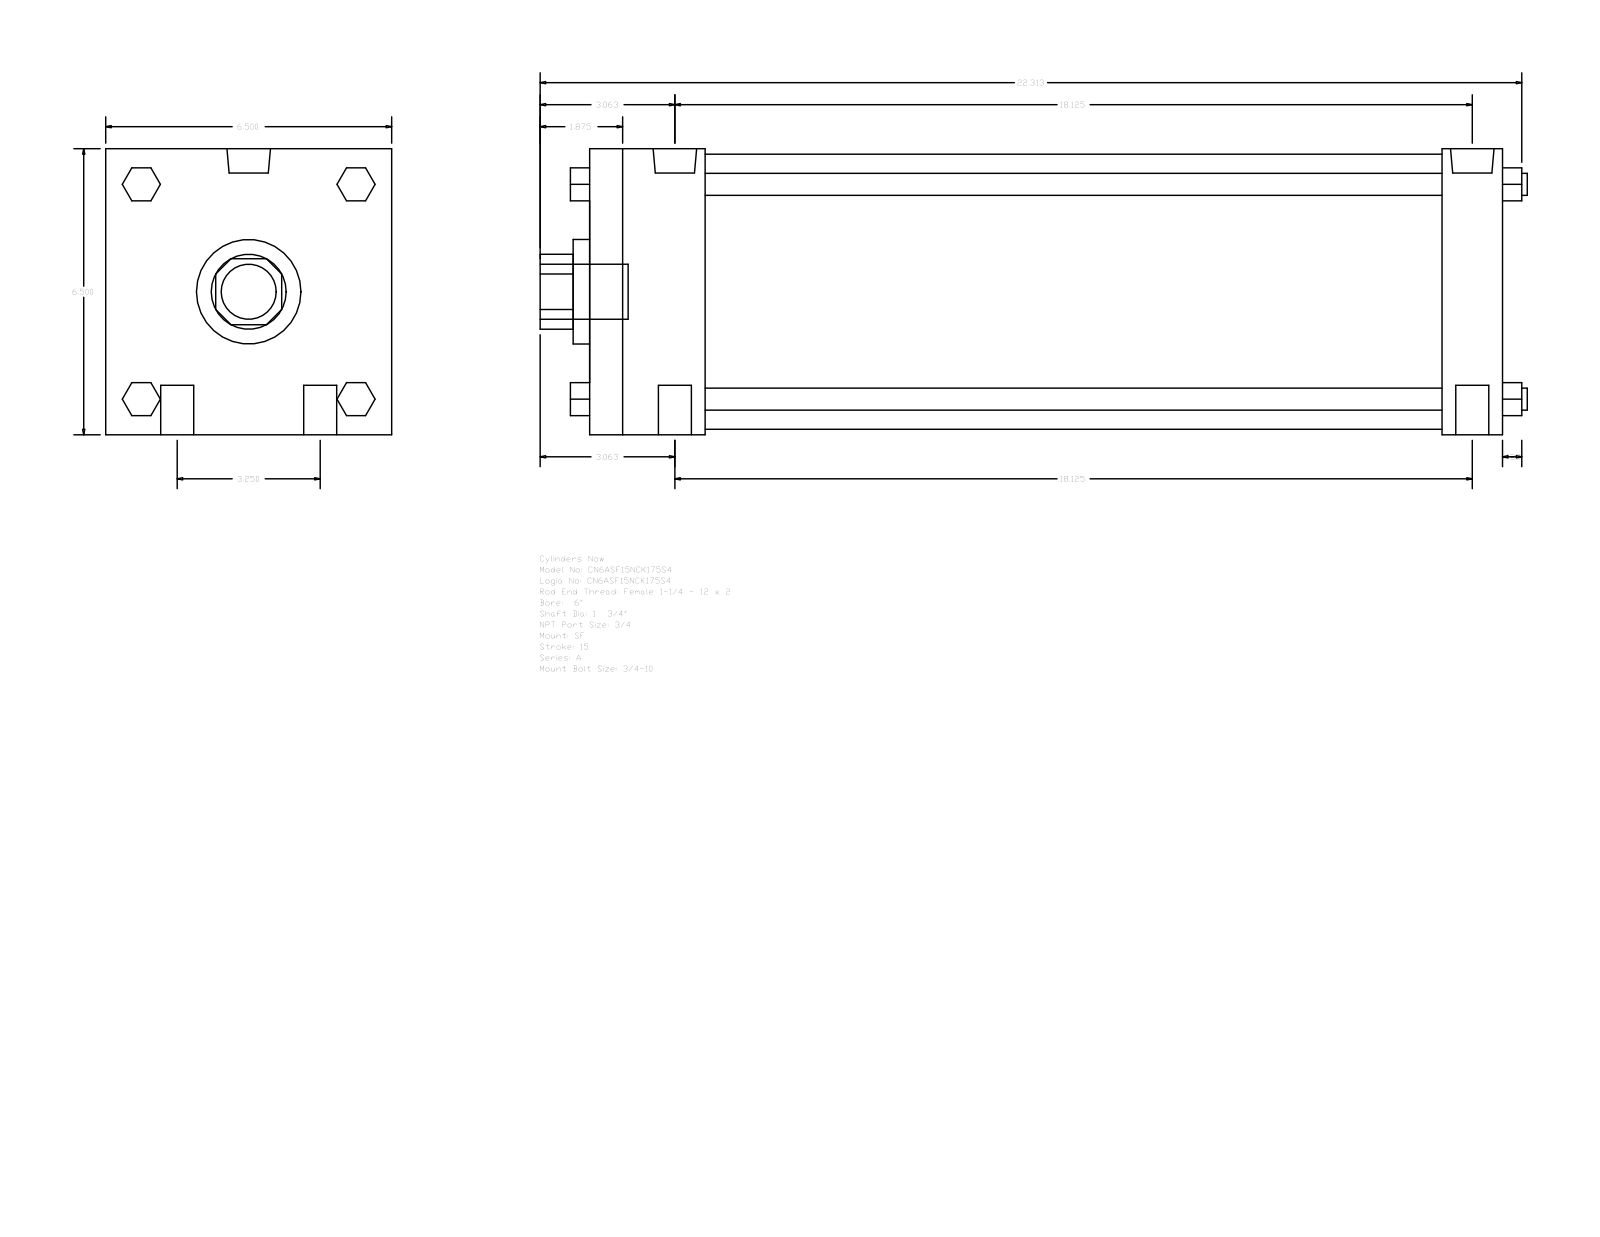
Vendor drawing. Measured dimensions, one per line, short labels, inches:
name: A_SF__0600_1.75
written by: GSSL Pune (CONFIG_CONTROL_DESIGN)
unit: in
bodies: 0 solids, 124 faces (94 planar, 30 cylindrical, 0 other)
size: 22.437 × 6.5 × 6.5
holes: 1× ⌀1.75, 1× ⌀2.375, 1× ⌀6.25
bosses: 4× ⌀0.75, 4× ⌀0.5, 2× ⌀0.989, 2× ⌀0.594, 1× ⌀1.25
rounds: 1× R0.852
face distances: 6.5, 20.75, 1.375, 19.375, 2.625, 16.75, 18.125, 0.75, 2.44, 4.226
